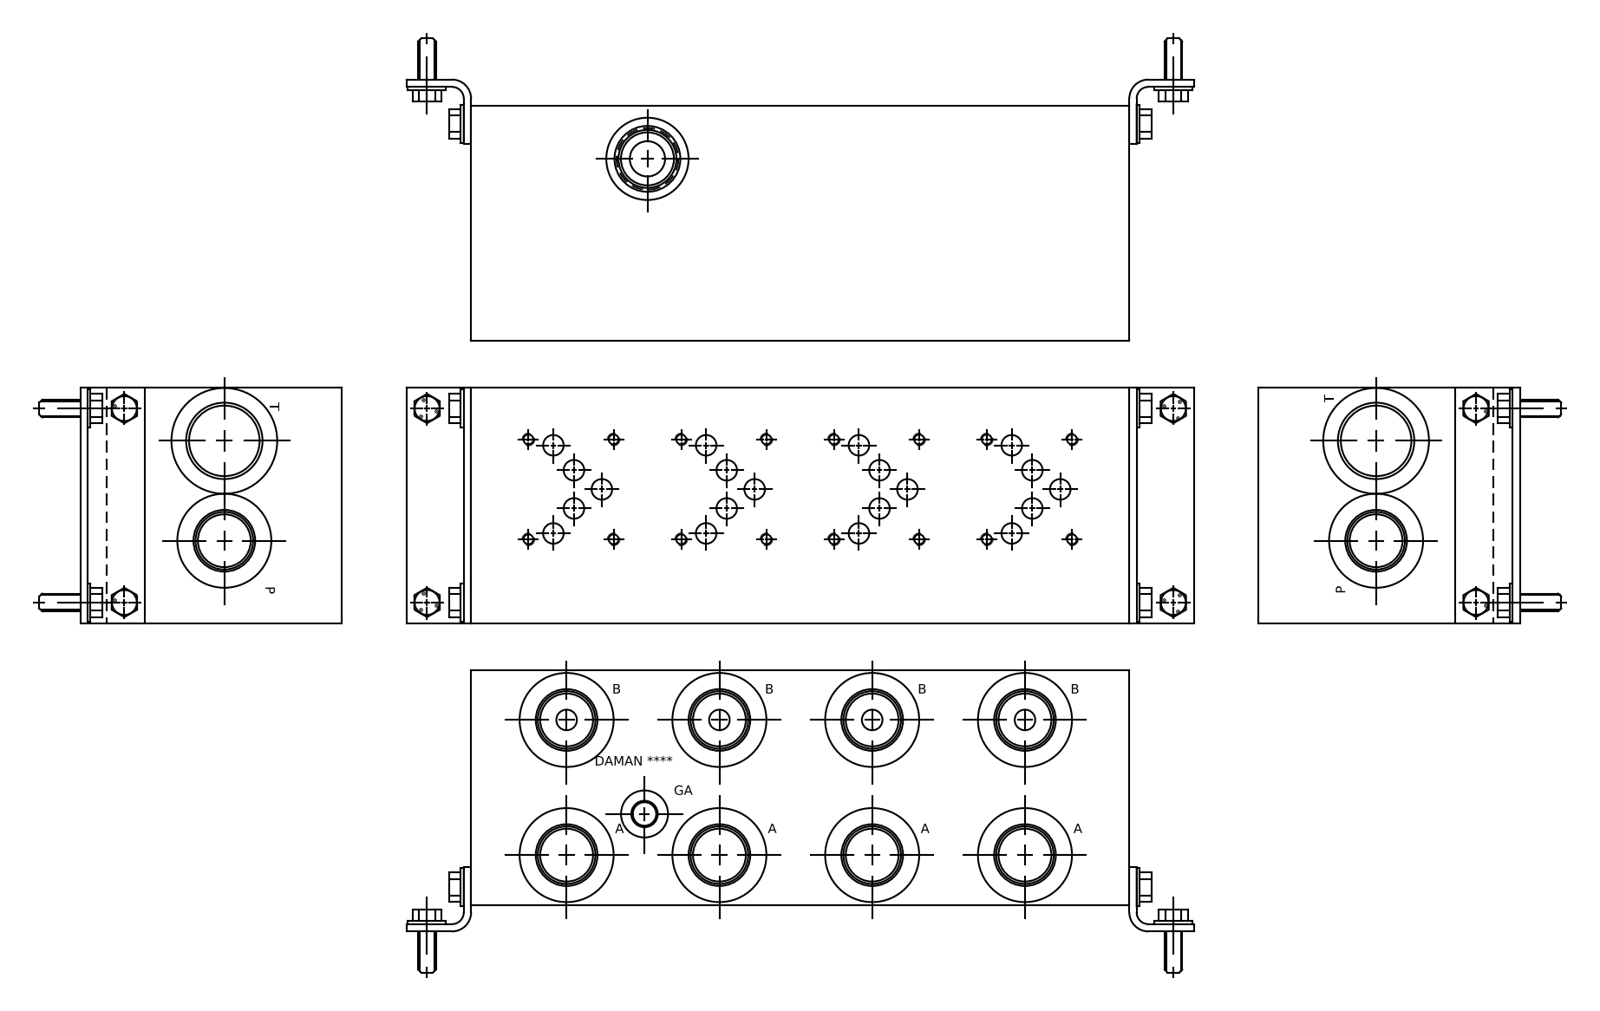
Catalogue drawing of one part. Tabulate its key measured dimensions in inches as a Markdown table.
| quantity | value |
| --- | --- |
| part name | Part_DD05JP043S~C_3D |
| STEP written by | Autodesk Inventor 2019 (AUTOMOTIVE_DESIGN) |
| units | inches |
| bodies | 1 solid, 866 faces (428 planar, 138 cylindrical, 300 other) |
| overall size | 14 × 5 × 5 |
| volume | 321.2 in³ |
| surface area | 431.7 in² |
| round holes (diameter × count) | 0.201 × 16, 0.25 × 16, 1.313 × 10, 1.231 × 9, 1.329 × 9, 1.928 × 9, 0.406 × 8, 0.438 × 8, 1.125 × 8, 1.398 × 7, 0.375 × 6, 0.312 × 2 |
| main face-to-face distances | 5, 0.031, 14, 4.969, 13.969, 13.938, 0.75, 0.781, 4.219, 13.219 |
| hole center spacings | 3.25, 6.5, 9.75, 2.374, 2.863, 3.35, 0.72, 1.394 |
